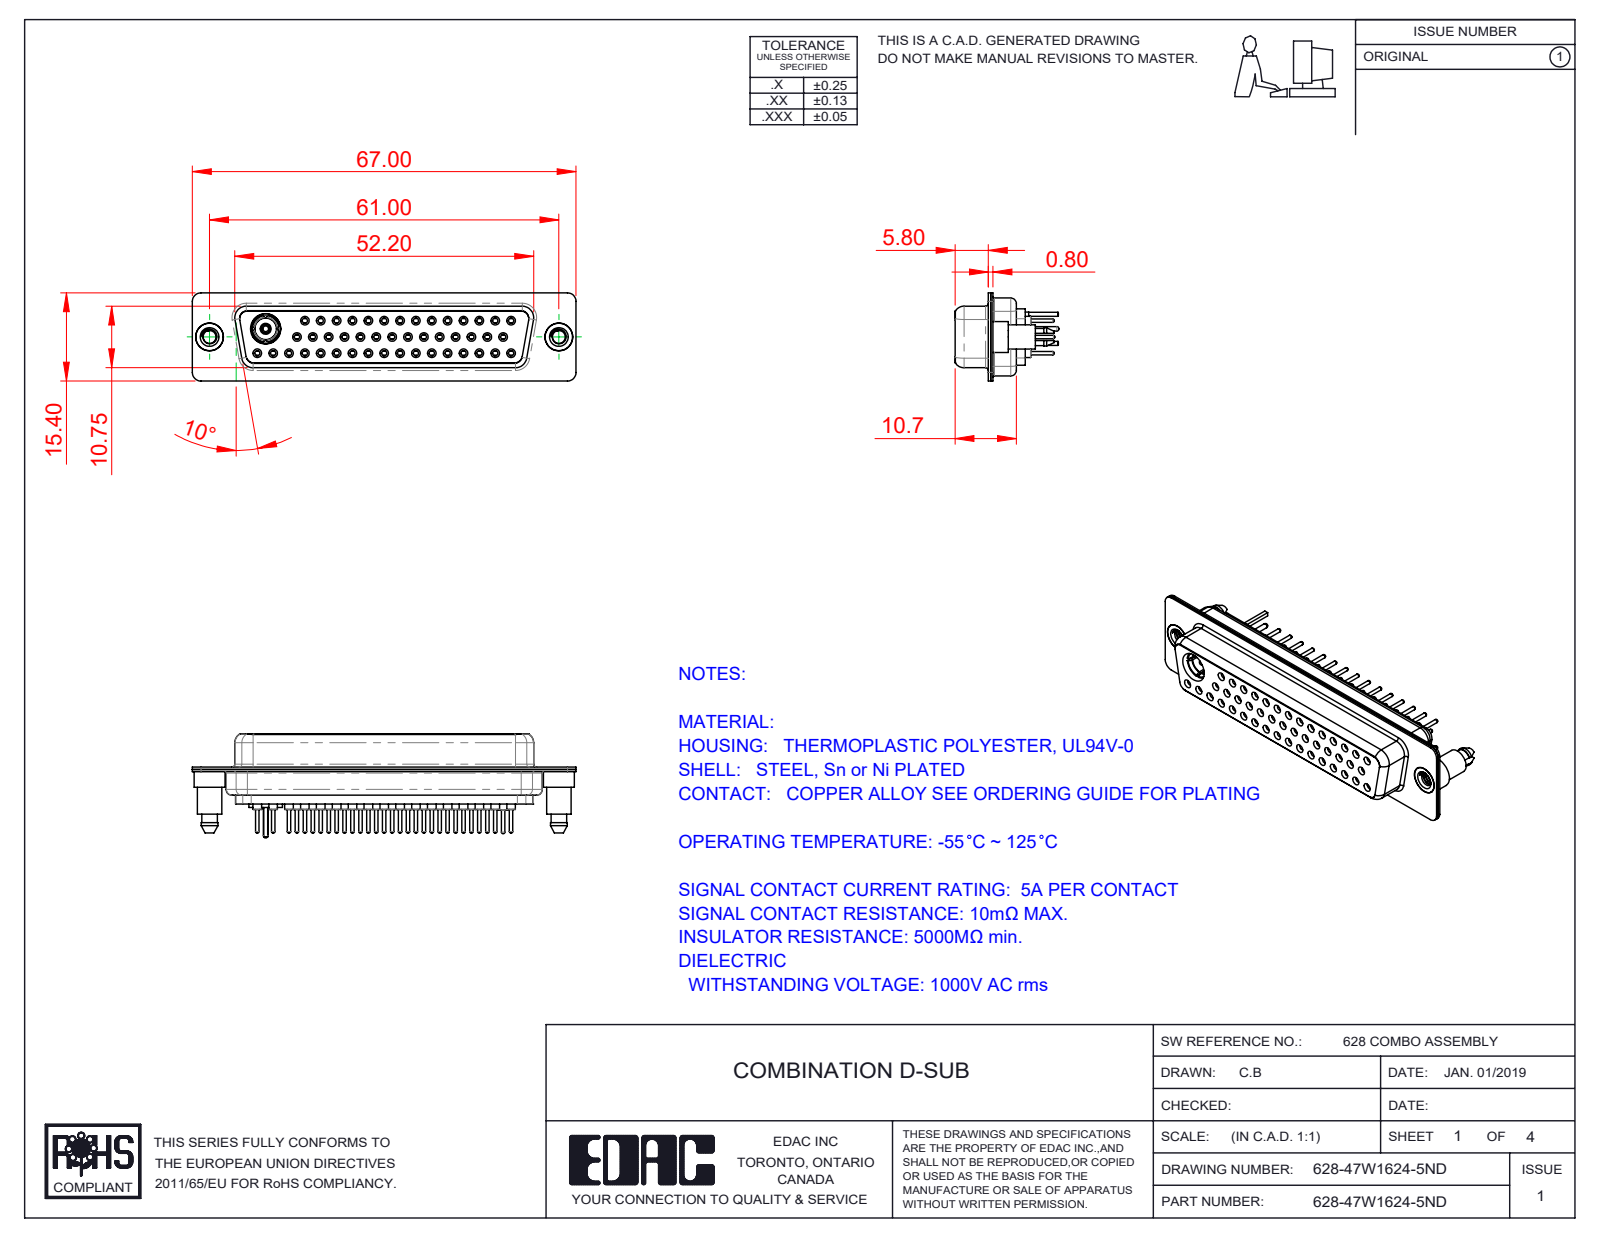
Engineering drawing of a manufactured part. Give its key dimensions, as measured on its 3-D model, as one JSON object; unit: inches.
{"part_name": "628Combo Shell Rear_50 Contacts; 628-47W1624-5ND; 628Combo Contact Row 1_24; Pin_Str (+8 more)", "step_written_by": "SolidWorks 2016 (CONFIG_CONTROL_DESIGN)", "units": "inches", "bodies": {"solids": 55, "faces": 2989, "planar": 827, "cylindrical": 1096, "other": 1066}, "overall_size": [2.638, 0.715, 0.606], "volume_in3": 0.438, "surface_area_in2": 23.59, "round_holes": [[0.043, 47], [0.059, 46], [0.035, 45], [0.079, 45], [0.063, 31], [0.067, 14], [0.191, 3], [0.089, 2], [0.157, 2], [0.159, 2], [0.111, 1], [0.13, 1]], "round_bosses_or_shafts": [[0.087, 46], [0.024, 46], [0.063, 15], [0.213, 2], [0.195, 2], [0.189, 2], [0.167, 2], [0.23, 1]], "partial_cylinders_radius": [[0.059, 18], [0.053, 12], [0.079, 12], [0.063, 10], [0.01, 4], [0.02, 4], [0.024, 4], [0.026, 4]], "face_to_face_distances": [0.016, 0.238, 0.254, 0.446, 0.074, 0.482, 0.244, 0.228, 0.407, 0.43], "hole_center_spacings": [0.124, 0.109, 0.218, 0.327, 0.436, 0.545, 0.654, 0.763]}
